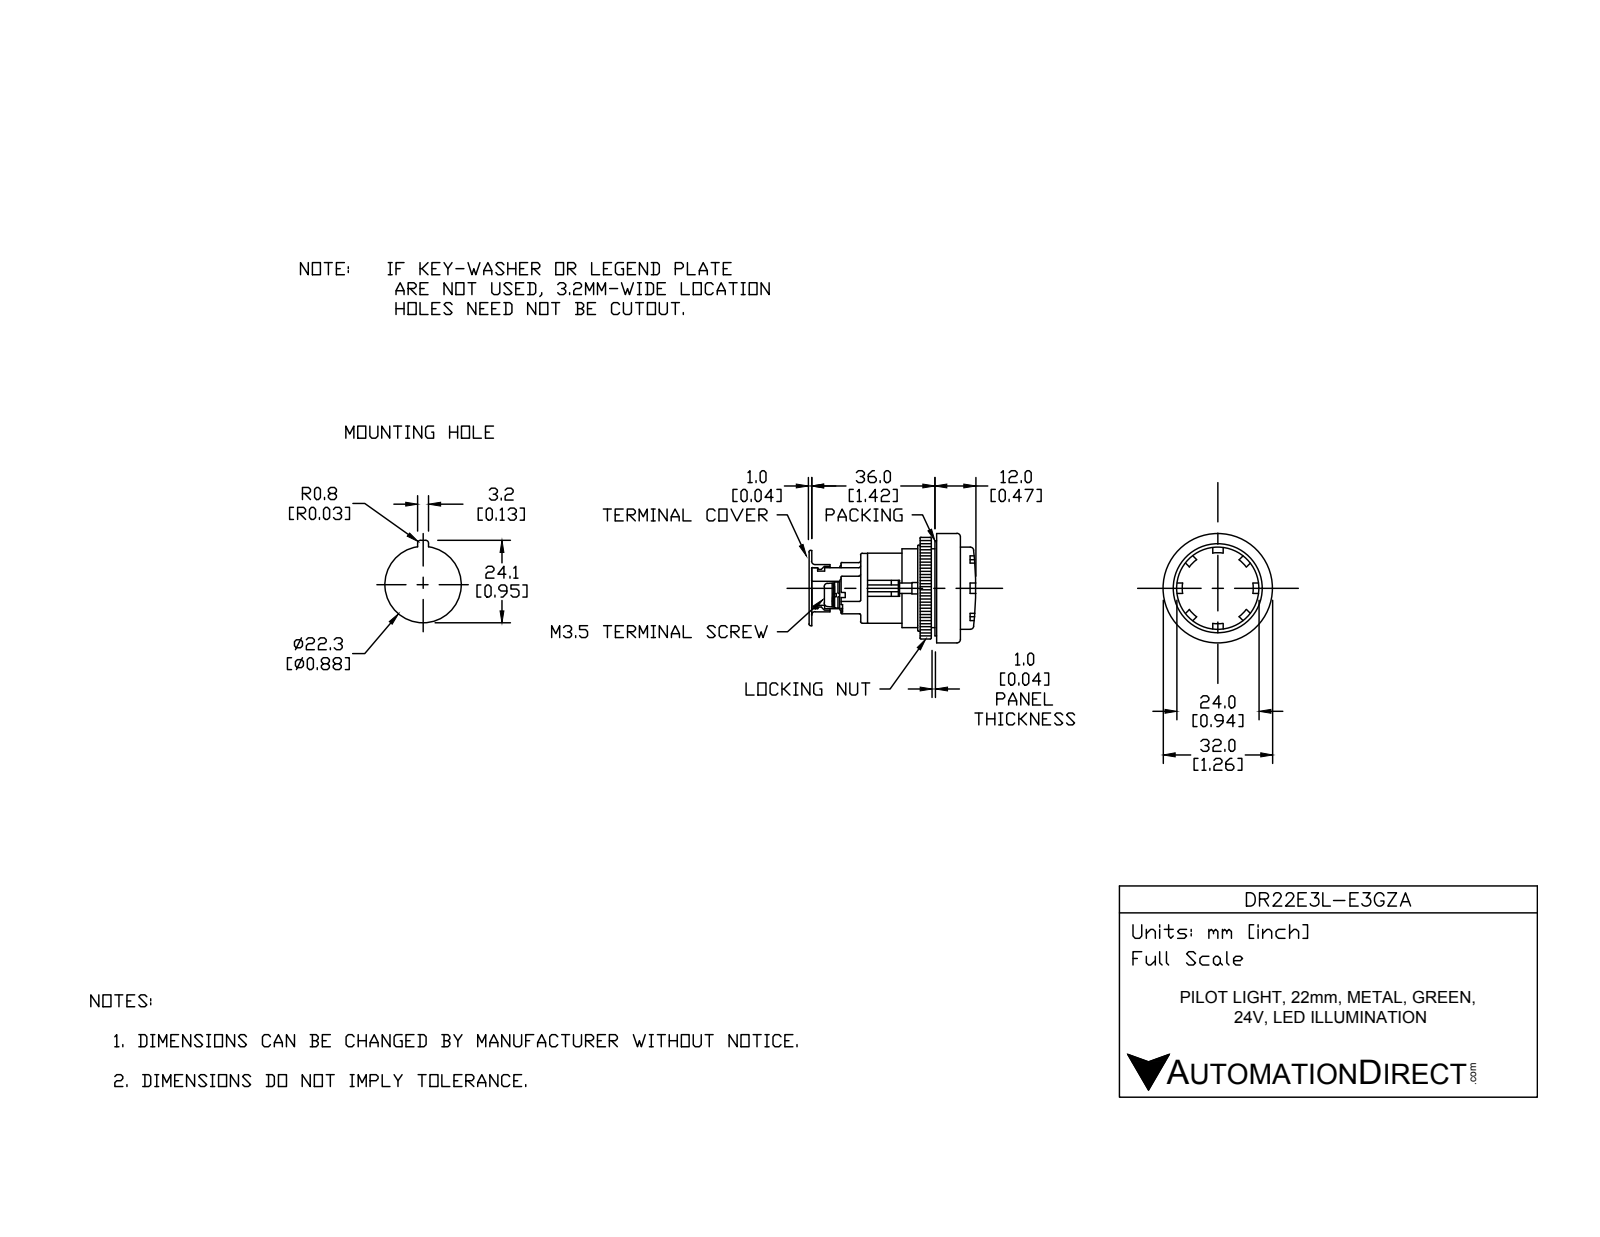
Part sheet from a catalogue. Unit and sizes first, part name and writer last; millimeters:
Units: millimetres
Overall size (bounding box): 48 × 32 × 32
Round holes (diameter × count): ⌀6.4 ×2, ⌀22 ×1, ⌀25 ×1, ⌀30 ×1
Round bosses / shafts (diameter × count): ⌀5.8 ×2, ⌀32 ×1, ⌀29.7 ×1, ⌀29.5 ×1, ⌀27 ×1, ⌀21.8 ×1
Partial cylindrical surfaces — rounded edges, fillets, slot ends (radius × count): R0.5 ×8
Main face-to-face distances: 4, 26, 6, 16, 1, 20, 27, 42, 15, 11
Hole centre spacings: 6.04, 12.08
Volume: 19 463 mm³ · Surface area: 11 440 mm²
Bodies: 11 solids, 126 faces (76 planar, 38 cylindrical, 12 other)
Part name (STEP PRODUCT): DR22E3L-E3GZA
STEP written by: SolidWorks 2017 (AUTOMOTIVE_DESIGN)
